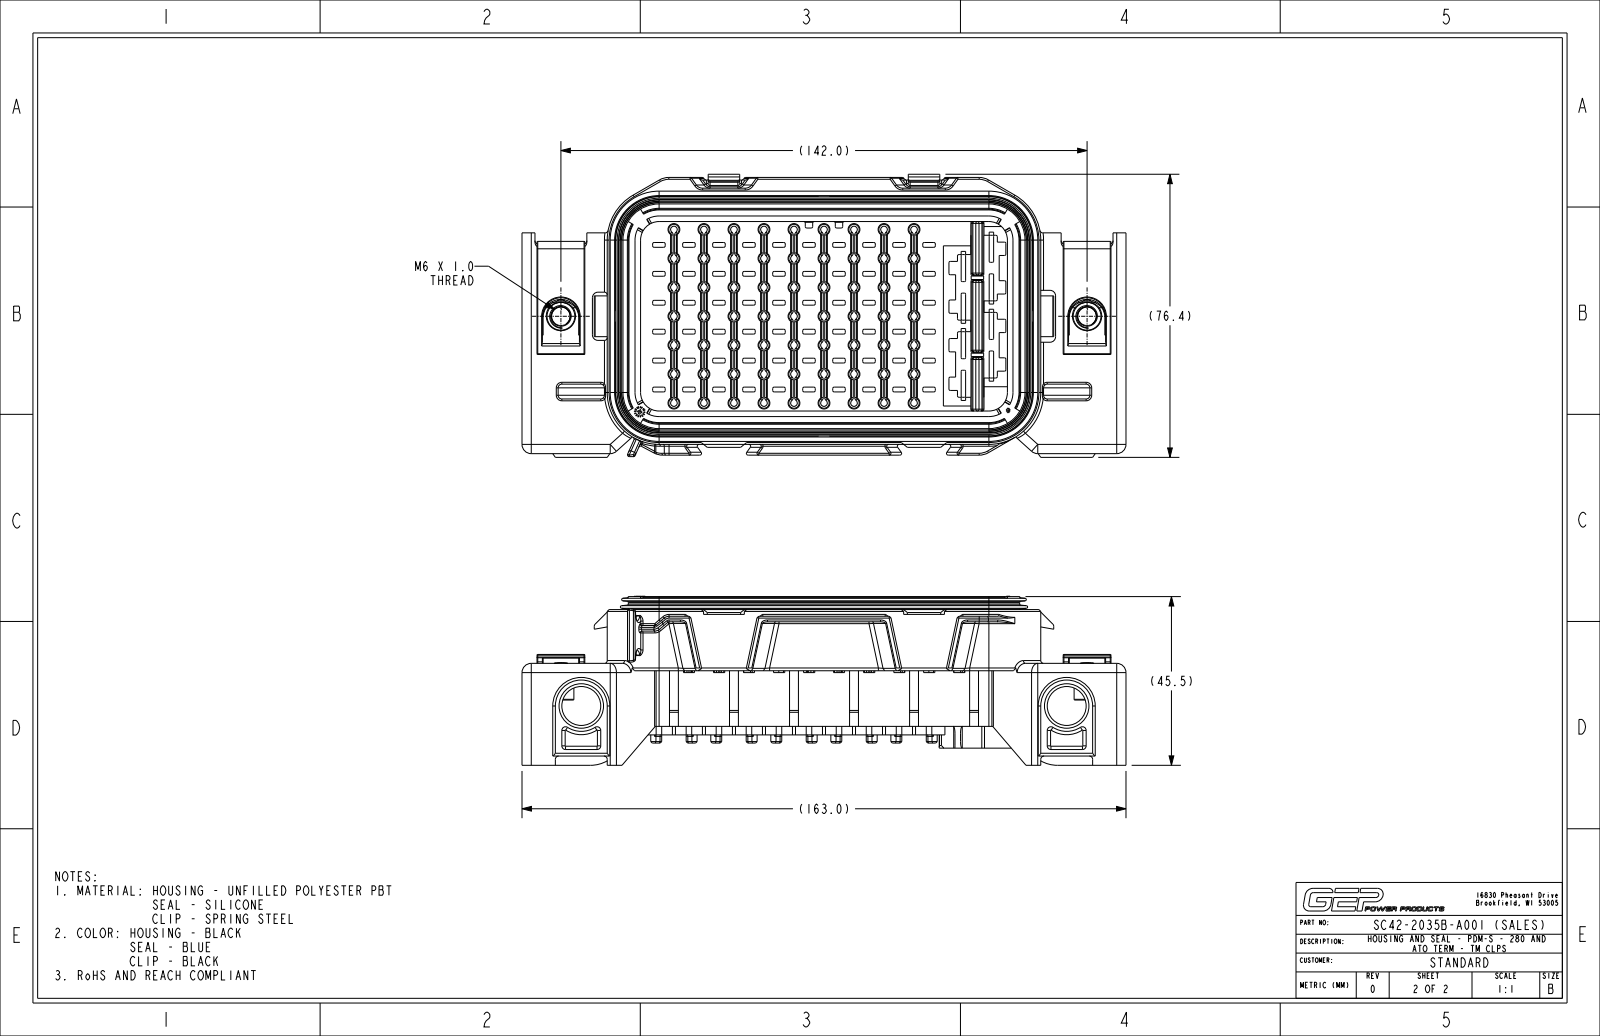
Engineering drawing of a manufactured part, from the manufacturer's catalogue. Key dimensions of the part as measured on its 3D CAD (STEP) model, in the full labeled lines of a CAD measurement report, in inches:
Part name (STEP PRODUCT): SC42-2035B-A001_NCF_SW0001
STEP written by: CREO PARAMETRIC BY PTC INC, 2024014 (CONFIG_CONTROL_DESIGN)
Units: inches
Bodies: 1 solid, 7736 faces (2300 planar, 2150 cylindrical, 3286 other)
Overall size (bounding box): 6.417 × 3.006 × 1.795
Volume: 10.31 in³ · Surface area: 179.1 in²
Round holes (diameter × count): ⌀0.264 ×60, ⌀0.335 ×8, ⌀0.413 ×4, ⌀0.197 ×2, ⌀0.295 ×2, ⌀0.492 ×2
Round bosses / shafts (diameter × count): ⌀0.276 ×2, ⌀0.157 ×1
Partial cylindrical surfaces — rounded edges, fillets, slot ends (radius × count): R0.02 ×678, R0.016 ×294, R0.012 ×84, R0.055 ×63, R0.175 ×60, R0.008 ×52, R0.035 ×38, R0.014 ×36
Main face-to-face distances: 0.079, 0.217, 0.059, 0.295, 0.354, 0.276, 0.374, 0.453, 0.071, 0.098
Hole centre spacings: 0.692, 0.319, 0.885, 0.638, 1.137, 0.957, 0.614, 1.416
